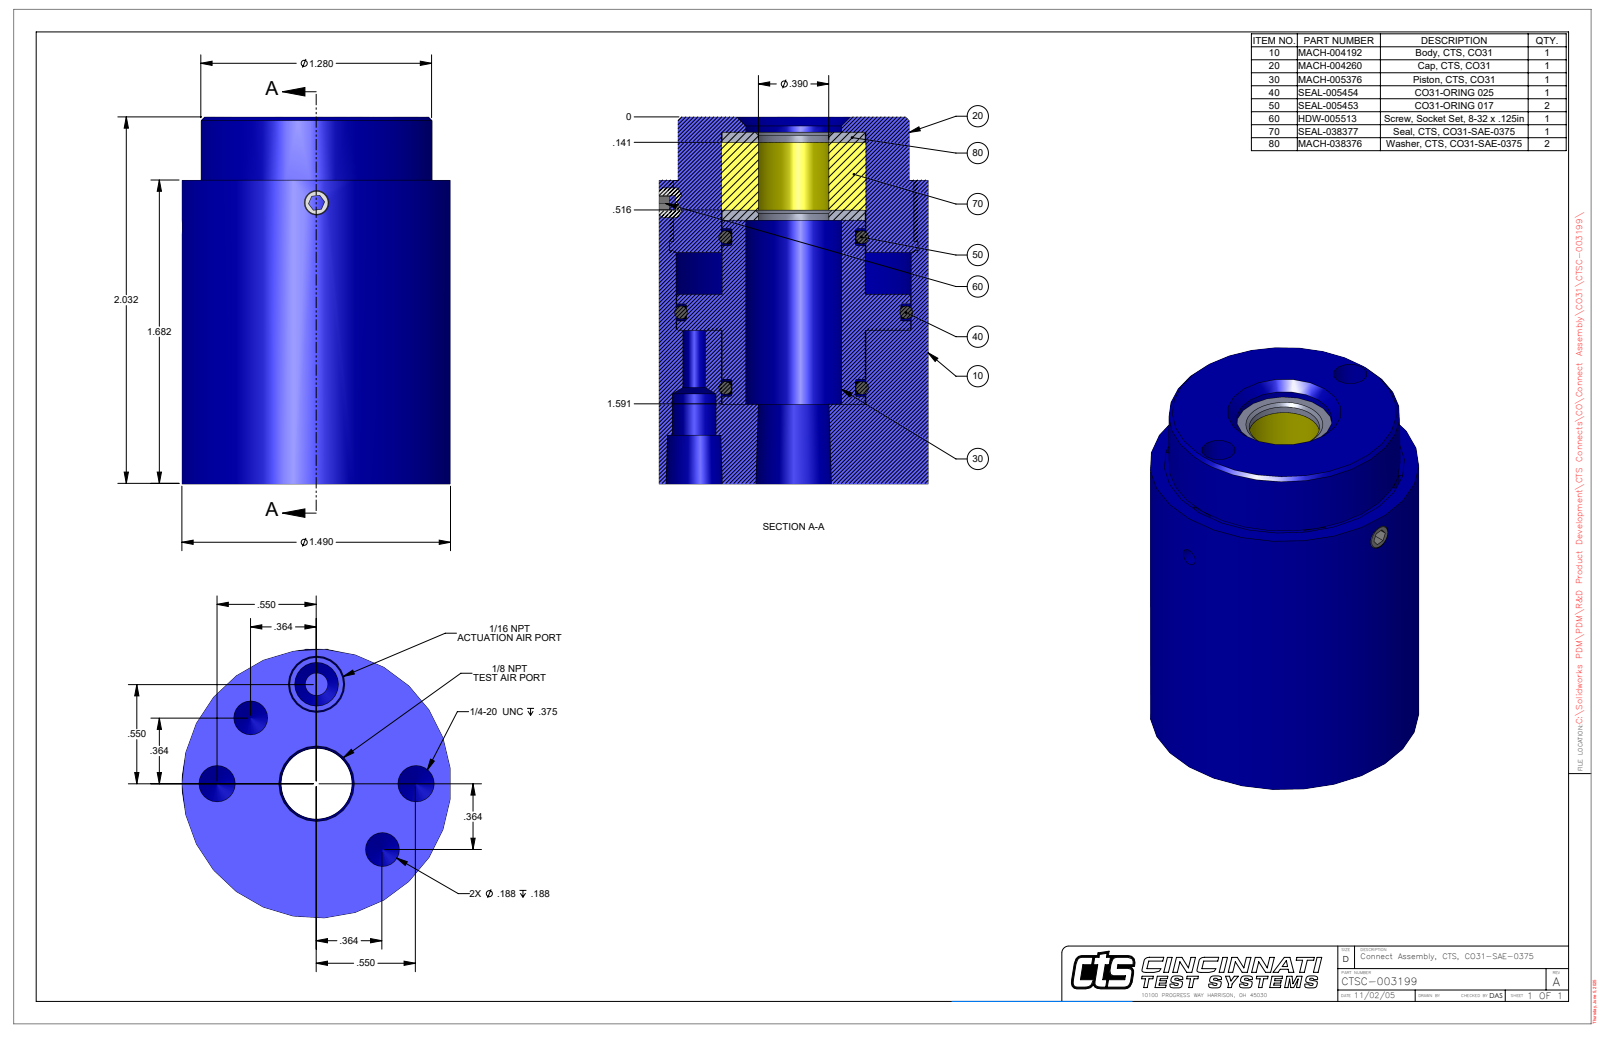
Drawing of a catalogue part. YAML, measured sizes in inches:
part_name: "CTSC-003199"
step_written_by: "SolidWorks 2023 (AUTOMOTIVE_DESIGN)"
units: inches
bodies: {solids: 1, faces: 108, planar: 52, cylindrical: 38, other: 18}
overall_size: [2.032, 1.49, 1.49]
volume: 2.959
surface_area: 17.09
round_holes:
  - {diameter: 0.187, count: 4}
  - {diameter: 0.201, count: 2}
  - {diameter: 0.094, count: 1}
  - {diameter: 0.136, count: 1}
  - {diameter: 0.242, count: 1}
  - {diameter: 0.39, count: 1}
  - {diameter: 0.53, count: 1}
  - {diameter: 0.8, count: 1}
  - {diameter: 1.33, count: 1}
round_bosses_or_shafts:
  - {diameter: 1.49, count: 1}
  - {diameter: 1.28, count: 1}
  - {diameter: 0.79, count: 1}
partial_cylinders:
  - {radius: 0.687, count: 1}
  - {radius: 0.734, count: 1}
face_to_face_distances: [2.032, 1.682, 0.35, 0.311, 1.371, 1.721, 1.46, 1.149, 0.222, 0.572]
hole_center_spacings: [0.515, 0.409, 0.55, 0.984, 0.035, 0.394, 0.754, 0.778]
